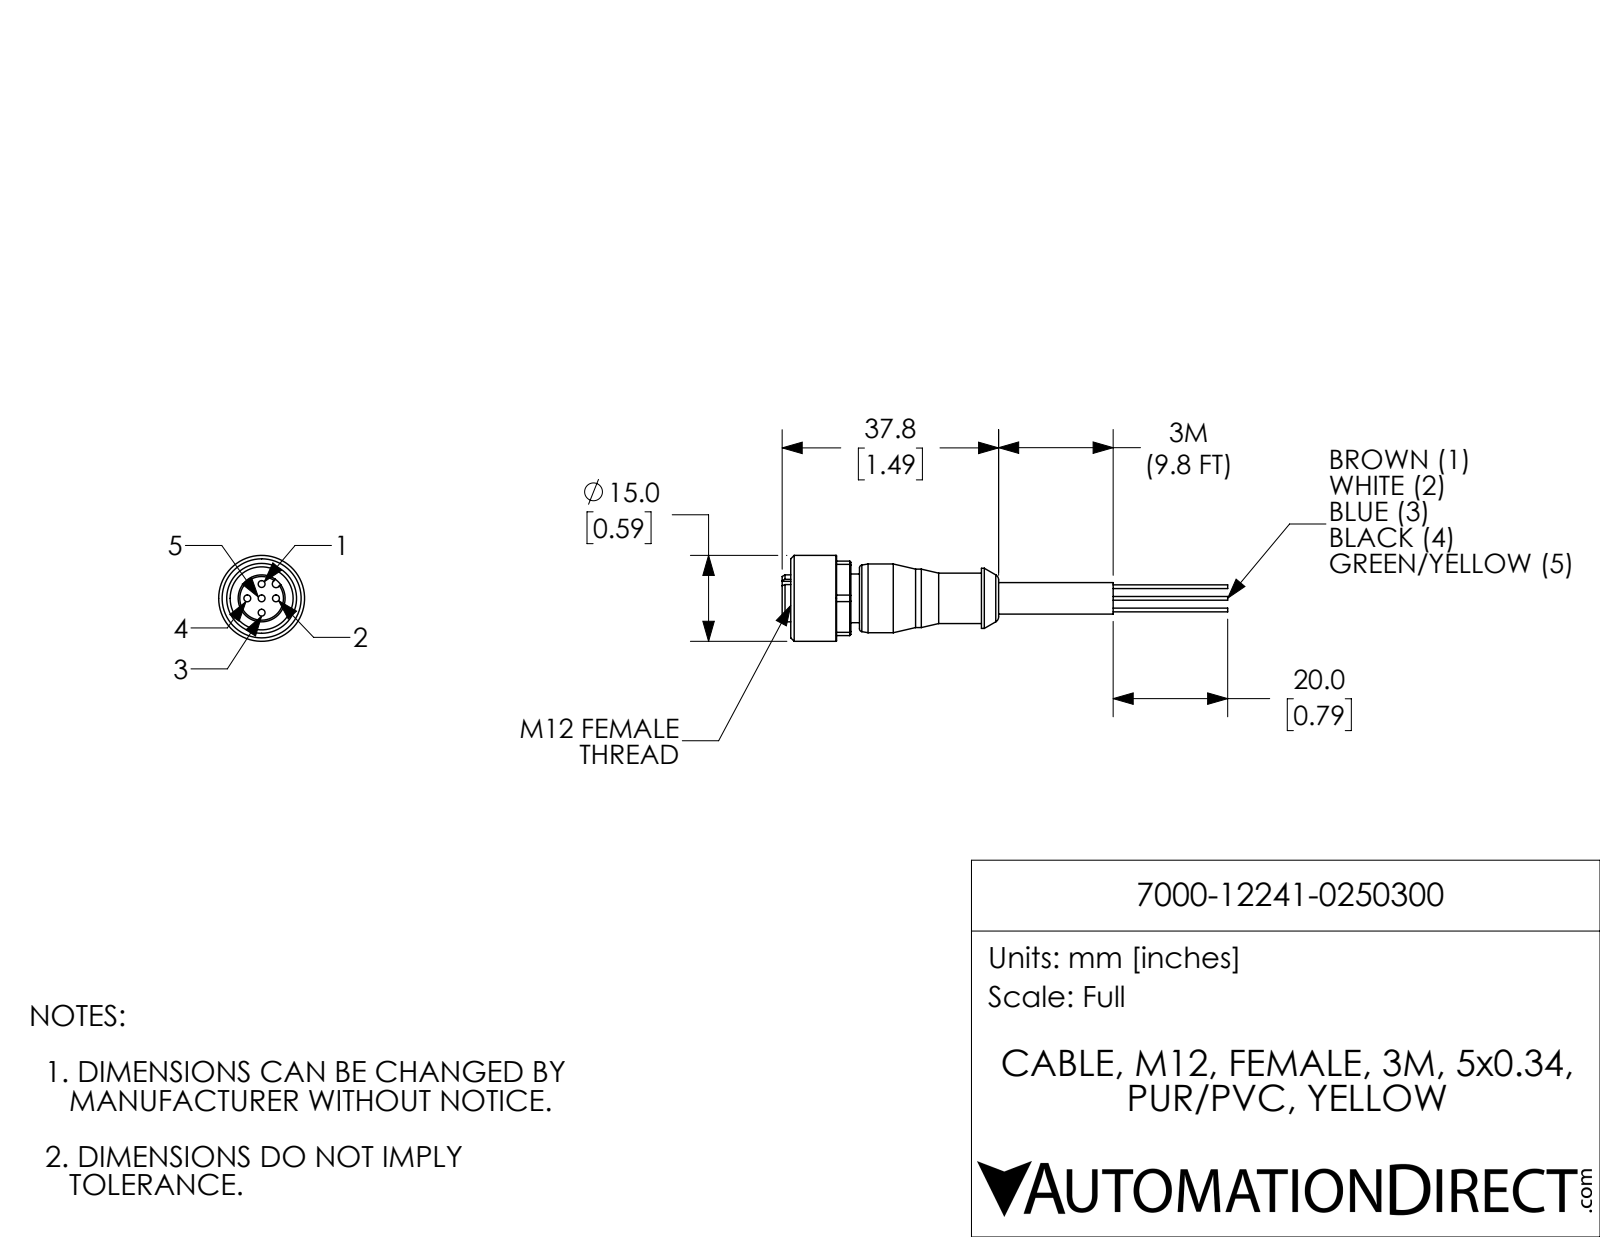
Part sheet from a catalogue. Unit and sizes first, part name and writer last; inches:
Units: inches
Overall size (bounding box): 3.063 × 0.591 × 0.591
Round holes (diameter × count): ⌀0.047 ×5, ⌀0.433 ×1
Round bosses / shafts (diameter × count): ⌀0.026 ×5, ⌀0.591 ×1, ⌀0.472 ×1, ⌀0.413 ×1, ⌀0.402 ×1, ⌀0.346 ×1, ⌀0.335 ×1, ⌀0.323 ×1
Partial cylindrical surfaces — rounded edges, fillets, slot ends (radius × count): R0.026 ×1, R0.283 ×1
Main face-to-face distances: 0.472, 0.059, 0.118, 0.512, 0.354, 1.016, 0.295, 0.413, 0.098, 0.531
Hole centre spacings: 0.098, 0.139, 0.197
Volume: 0.248 in³ · Surface area: 4.45 in²
Bodies: 1 solid, 106 faces (34 planar, 45 cylindrical, 27 other)
Part name (STEP PRODUCT): 7000-12241-0250300
STEP written by: SolidWorks 2017 (AUTOMOTIVE_DESIGN)
